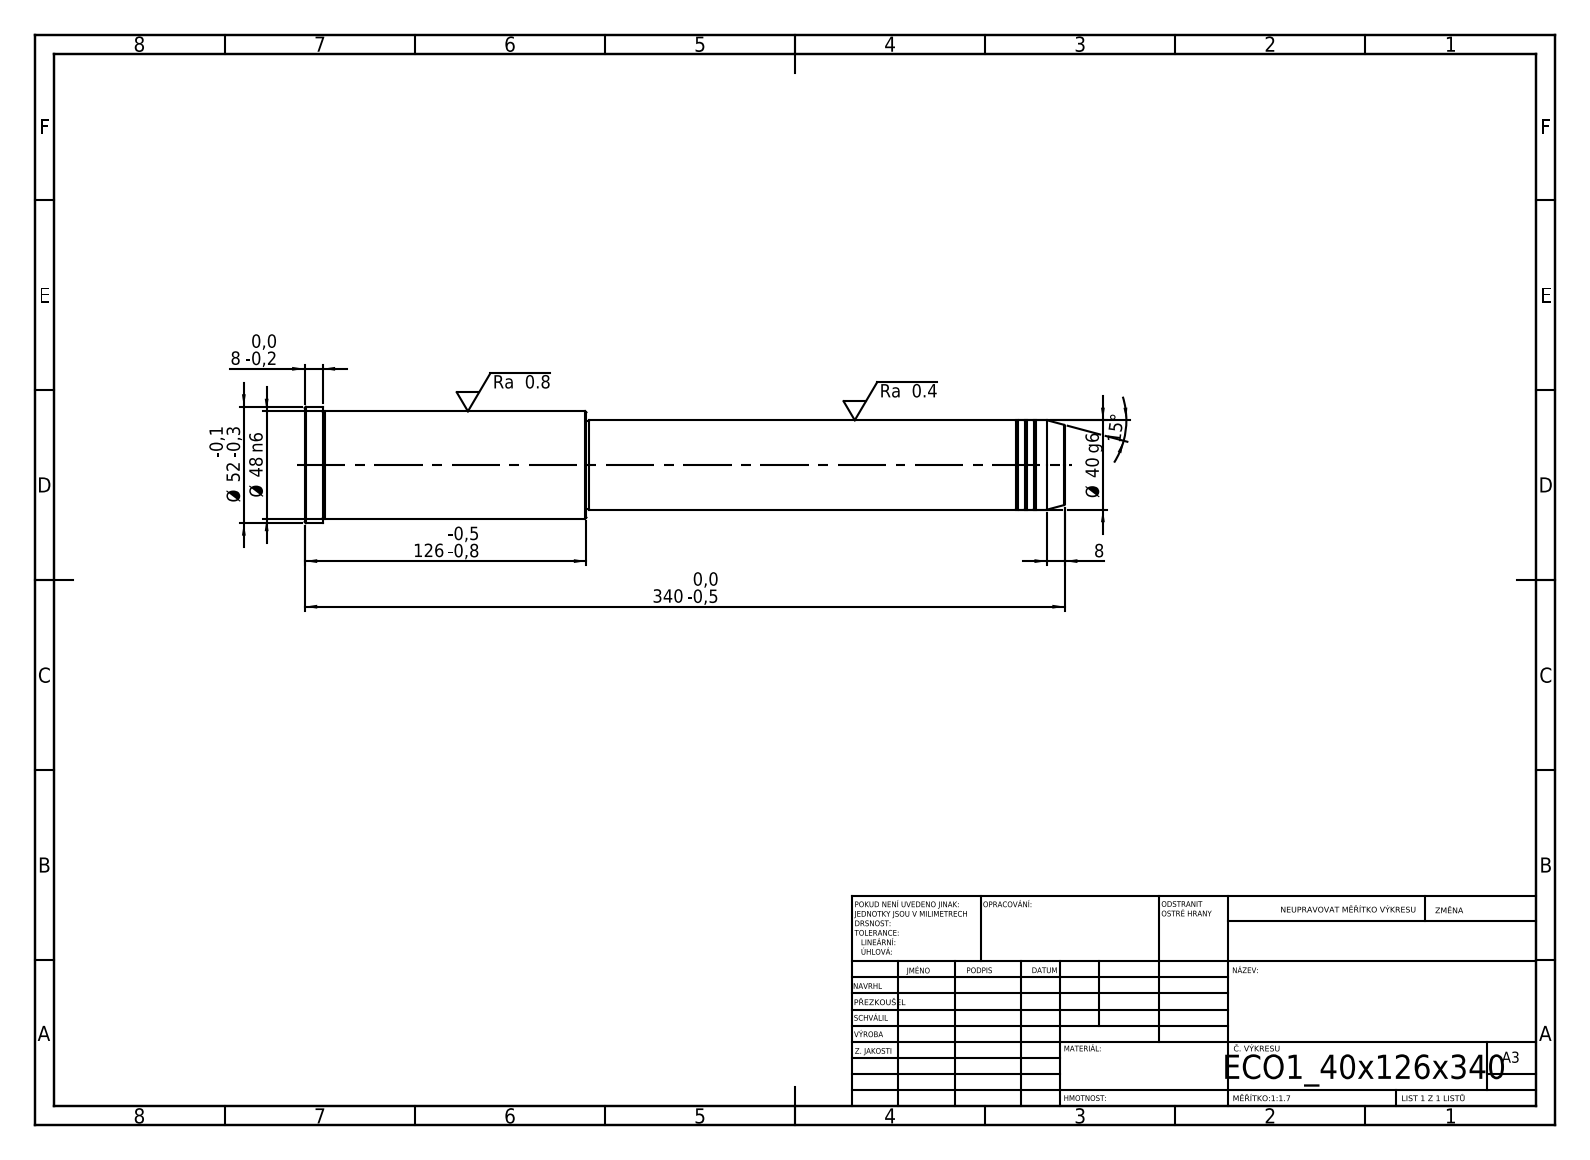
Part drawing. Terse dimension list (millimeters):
written by: SolidWorks 2019 (CONFIG_CONTROL_DESIGN)
unit: mm
bodies: 1 solid, 43 faces (5 planar, 14 cylindrical, 24 other)
size: 340 × 52 × 52
volume: 498 089 mm³; area: 50 269 mm²
bosses: 1× ⌀52, 1× ⌀48, 1× ⌀40, 1× ⌀39
face distances: 340, 214, 126, 332, 118, 8, 213, 1, 119, 127
